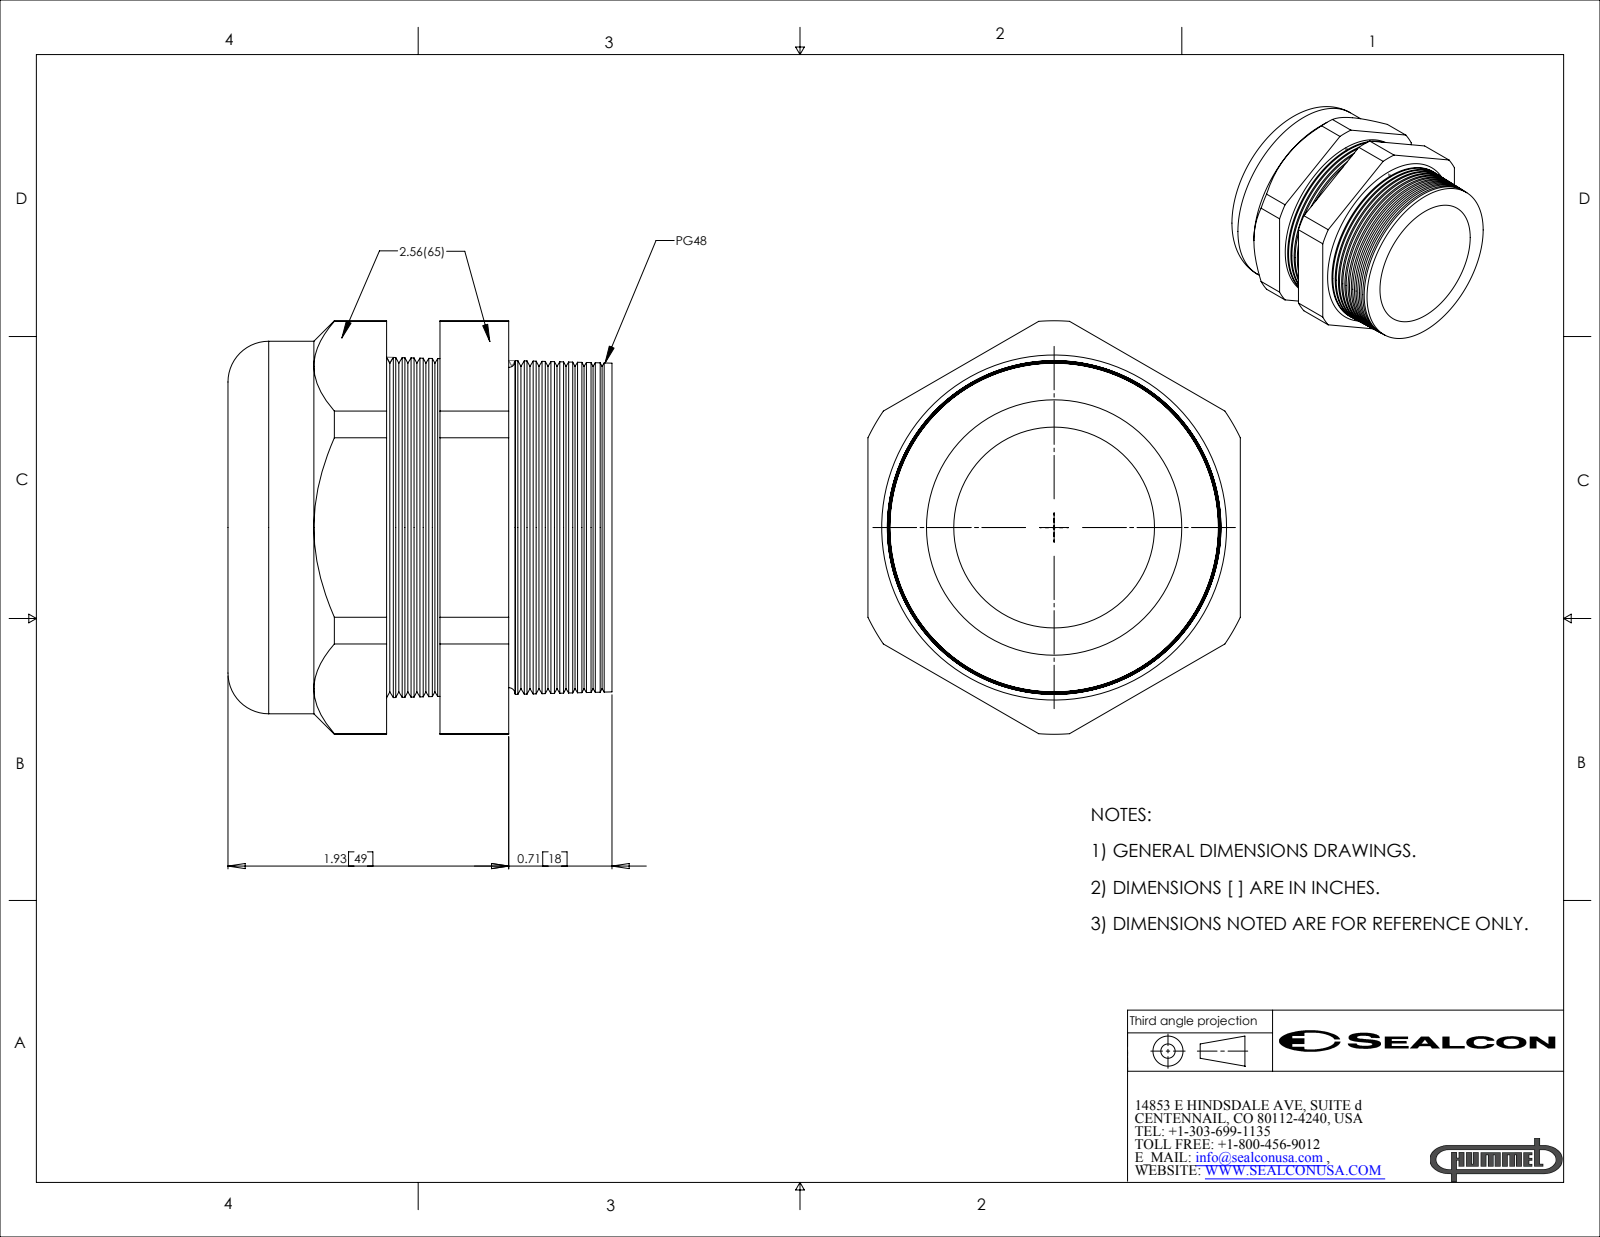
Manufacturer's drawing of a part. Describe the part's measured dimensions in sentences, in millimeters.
The part is named "CD48CR-BK". Its 3-D file was written by "SolidWorks 2007 (CONFIG_CONTROL_DESIGN)". It is 2 solids with 158 faces: 20 planar, 22 cylindrical and 116 other. Overall it measures 72.2 by 67.1 by 65 millimeters. Its volume is 132 100 cubic millimeters and its surface area 35 590 square millimeters. Round holes: 1 of diameter 35.1, 1 of diameter 44.6. Round bosses or shafts: 1 of diameter 65, 1 of diameter 44.6. Partial cylindrical surfaces (rounded edges, fillets, slot ends): 1 of radius 36.1. The main face-to-face distances are 65, 52.1, 22, 30, 12.7, 9.3, 39.4, 34, 21.3, 12.
